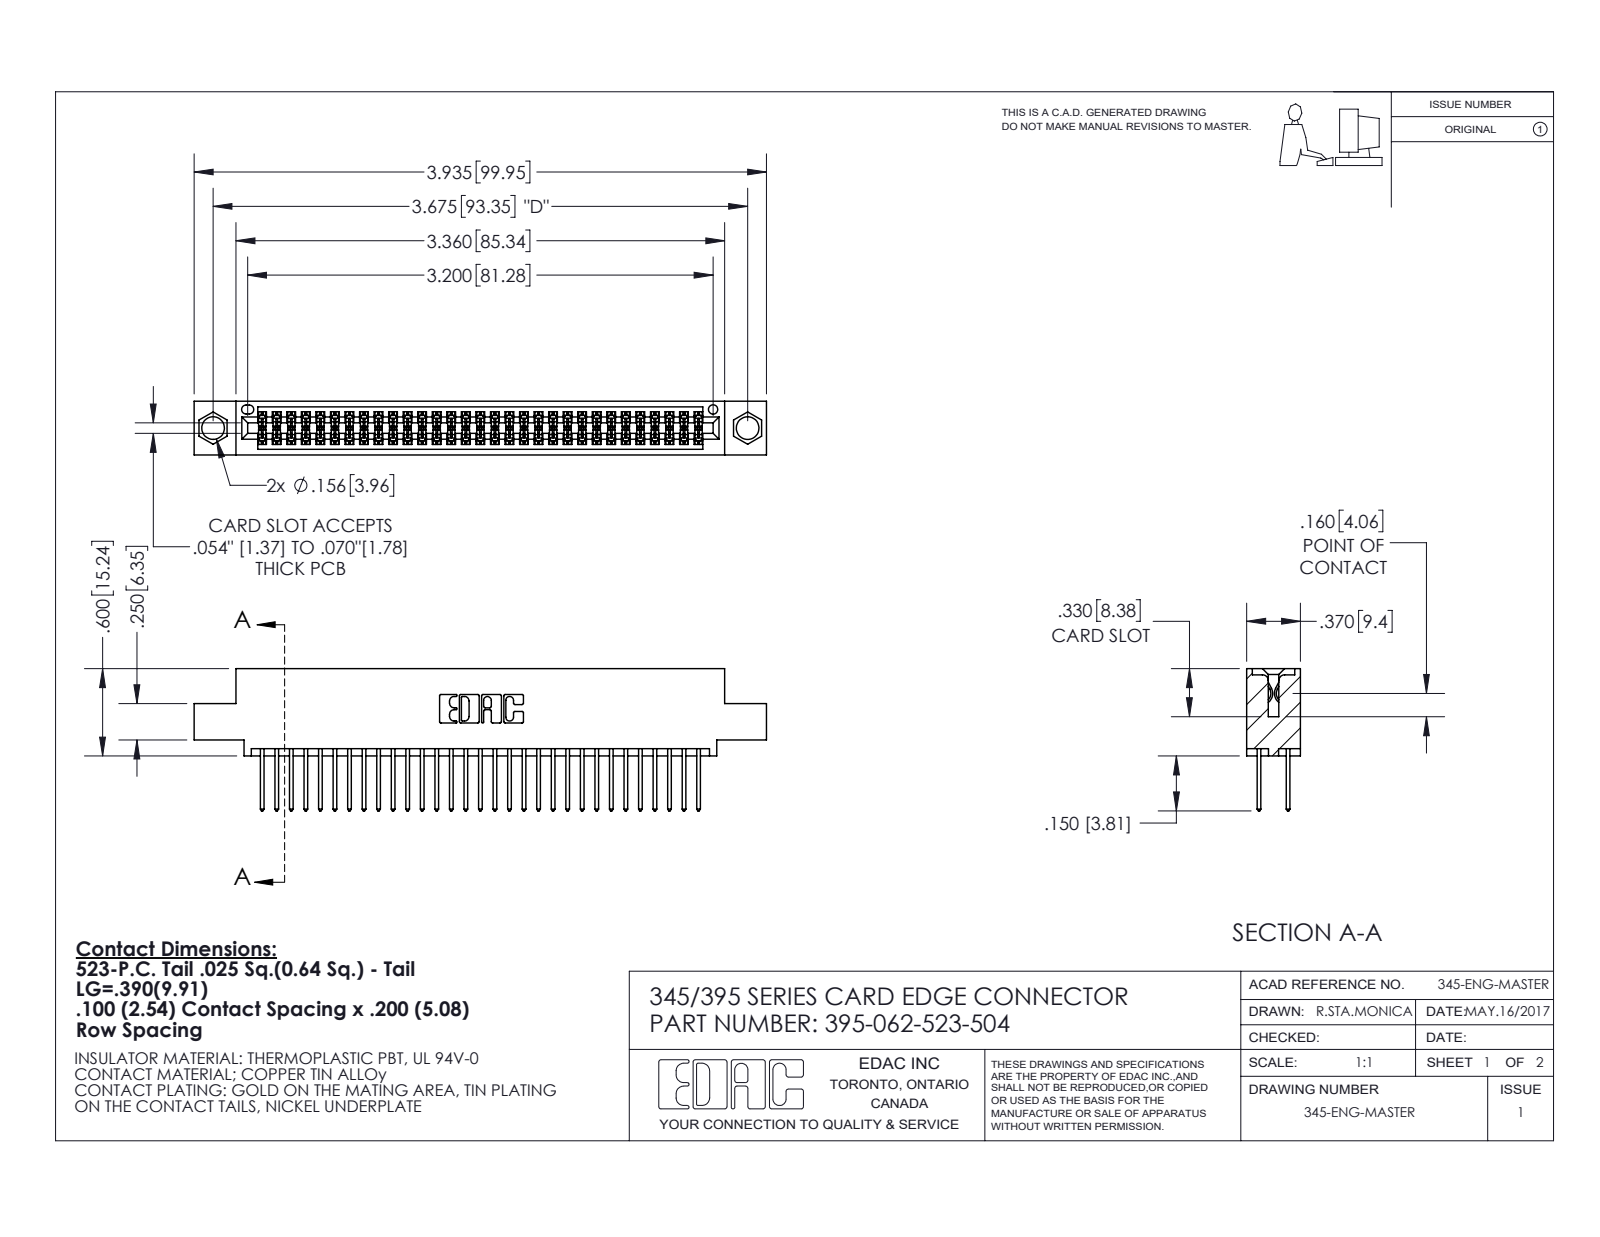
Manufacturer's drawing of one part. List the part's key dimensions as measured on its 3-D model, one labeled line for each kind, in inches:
Part name (STEP PRODUCT): 345 Part_0.110 Offset - 0.156 Dia-TI; 345-292-001_345-293-123; 395-062-523-504
STEP written by: SolidWorks 2020 (CONFIG_CONTROL_DESIGN)
Units: inches
Bodies: 63 solids, 3244 faces (2144 planar, 1100 cylindrical, 0 other)
Overall size (bounding box): 3.935 × 0.977 × 0.37
Volume: 0.583 in³ · Surface area: 22.36 in²
Round holes (diameter × count): ⌀0.156 ×2, ⌀0.064 ×1
Partial cylindrical surfaces — rounded edges, fillets, slot ends (radius × count): R0.006 ×124, R0.01 ×62, R0.01 ×22, R0.007 ×6, R0.031 ×6, R0.026 ×3, R0.014 ×2, R0.019 ×2
Main face-to-face distances: 0.072, 0.298, 0.2, 0.098, 0.272, 0.025, 0.37, 0.225, 0.175, 0.149
Hole centre spacings: 0.27, 3.44, 3.675
